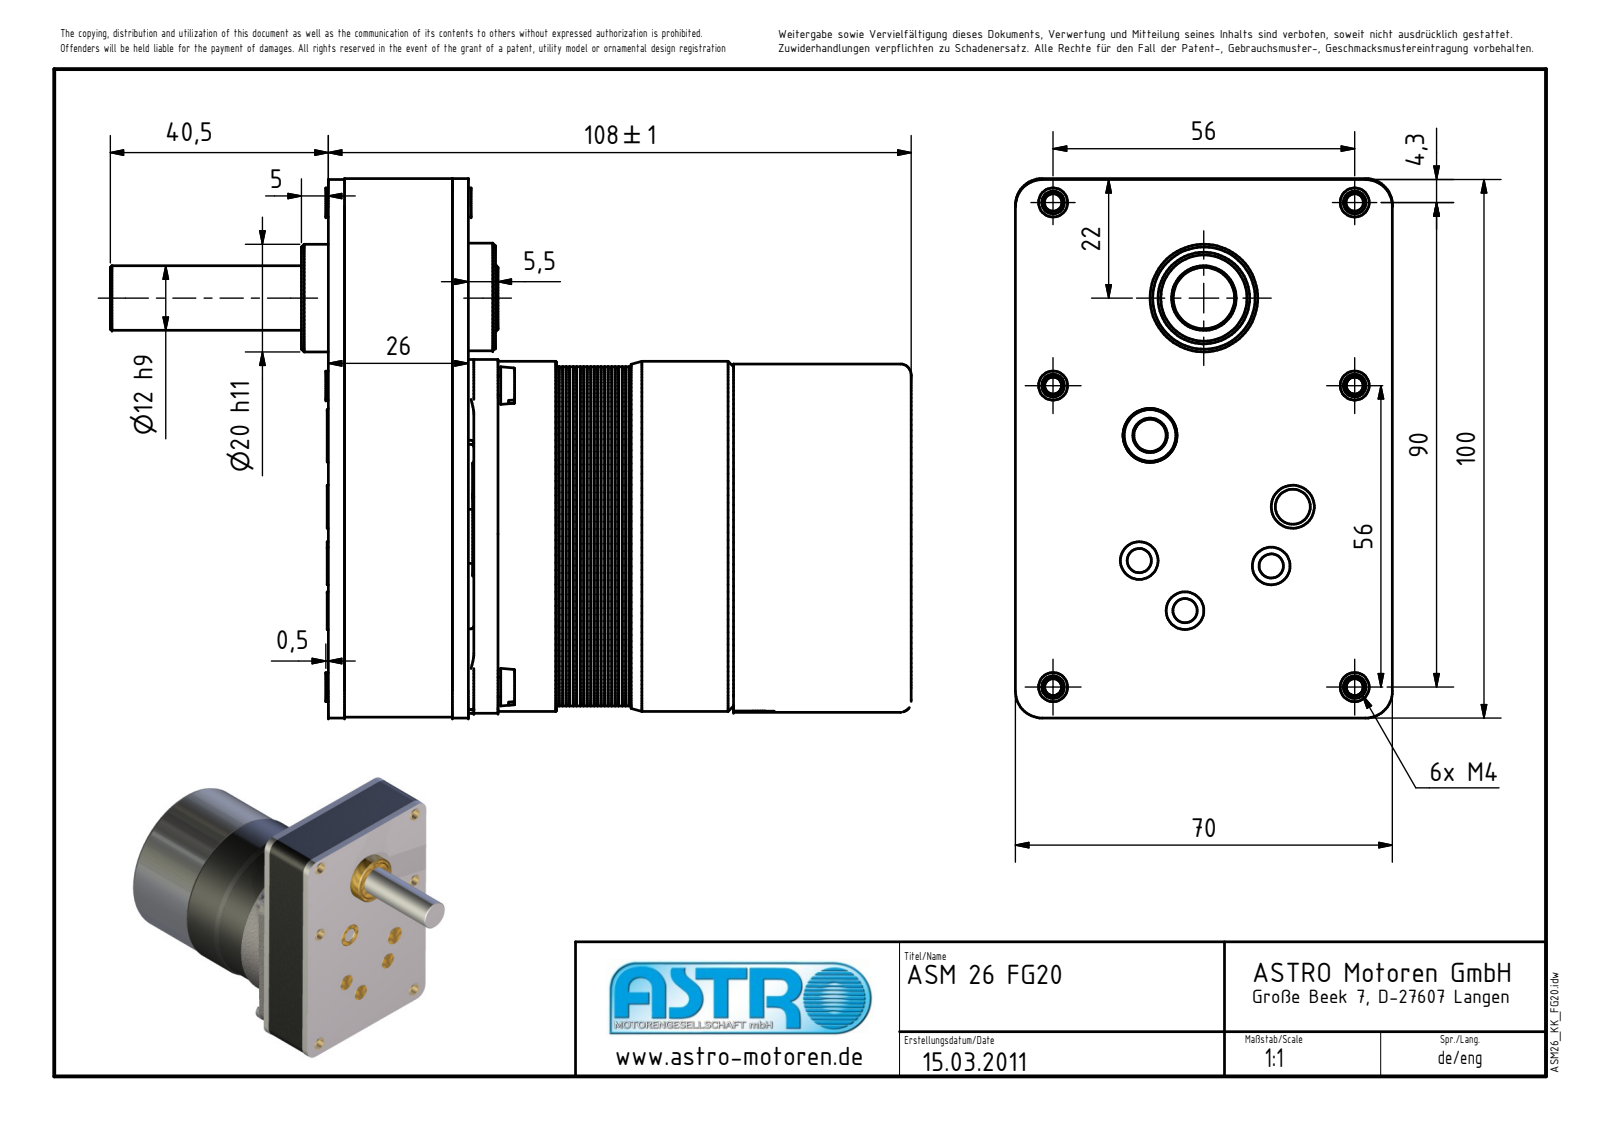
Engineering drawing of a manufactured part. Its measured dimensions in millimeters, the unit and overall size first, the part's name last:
Units: millimetres
Overall size (bounding box): 138.2 × 100 × 70
Round holes (diameter × count): ⌀3.24 ×11, ⌀4.2 ×10, ⌀1.6 ×8, ⌀4.1 ×8, ⌀5 ×8, ⌀4.5 ×5, ⌀4.4 ×4, ⌀8.5 ×4, ⌀6 ×3, ⌀10 ×3, ⌀2.46 ×2, ⌀16 ×2
Round bosses / shafts (diameter × count): ⌀8 ×9, ⌀5.39 ×6, ⌀4.84 ×6, ⌀15 ×4, ⌀4 ×4, ⌀3.57 ×4, ⌀8.5 ×3, ⌀7 ×3
Partial cylindrical surfaces — rounded edges, fillets, slot ends (radius × count): R0.5 ×37, R2.25 ×8, R3.5 ×8, R3.15 ×4, R5 ×4, R5.26 ×4, R2 ×3, R1 ×2
Main face-to-face distances: 0.65, 1.3, 3, 1.95, 2.6, 3.25, 23, 3.9, 20, 4.55
Hole centre spacings: 27, 56, 39.6, 38.18, 49.86, 55.87, 95.02, 9.73
Volume: 161 892 mm³ · Surface area: 190 078 mm²
Bodies: 52 solids, 4687 faces (1758 planar, 2848 cylindrical, 81 other)
Part name (STEP PRODUCT): ASM26_KK_FG20; AFG-20rund; FG-Abtriebsseite20_fürAbdeckungBlau; FG-Abtriebsseite20_fürAbdeckungBlau-Vorderseite (+8 more)
STEP written by: Autodesk Inventor 2017 (AUTOMOTIVE_DESIGN)
